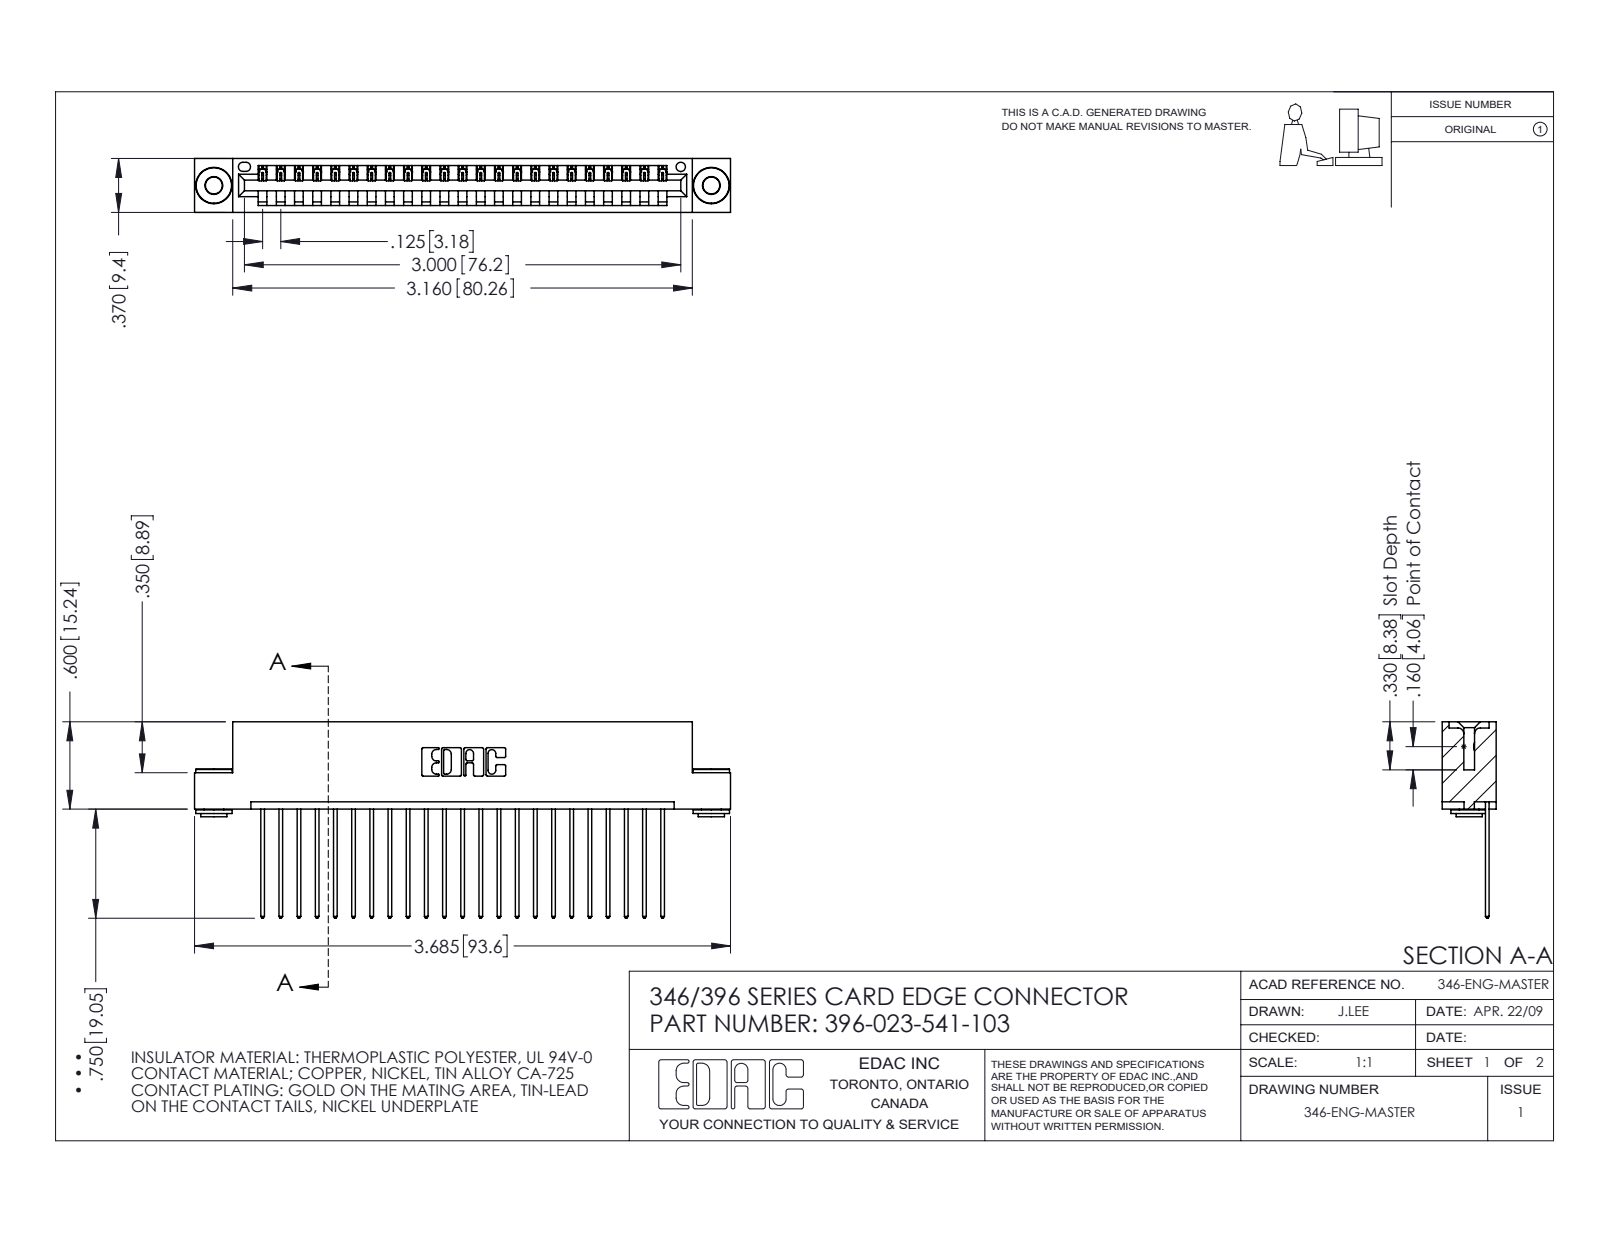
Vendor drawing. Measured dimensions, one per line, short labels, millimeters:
name: 346 Part_Flush Mounting Lugs - 0.156 Dia-TH; 345-250-002_345-250-002-102; 396-023-541-103; 345-292-001_345-293-141
written by: SolidWorks 2016 (CONFIG_CONTROL_DESIGN)
unit: mm
bodies: 26 solids, 1494 faces (1006 planar, 480 cylindrical, 8 other)
size: 93.6 × 34.3 × 9.4
volume: 8 930 mm³; area: 11 620 mm²
holes: 2× ⌀2.9, 2× ⌀4, 1× ⌀1.6
bosses: 2× ⌀6.4, 2× ⌀4.6, 2× ⌀3.5
rounds: 46× R0.2, 46× R0.3, 22× R0.3, 6× R0.2, 6× R0.8, 3× R0.7, 2× R0.8, 2× R1
face distances: 1.2, 8.2, 6.4, 9.4, 0.6, 1.8, 7.6, 3.8, 5.6, 2.5
hole spacings: 6.2, 81.6, 86.9
